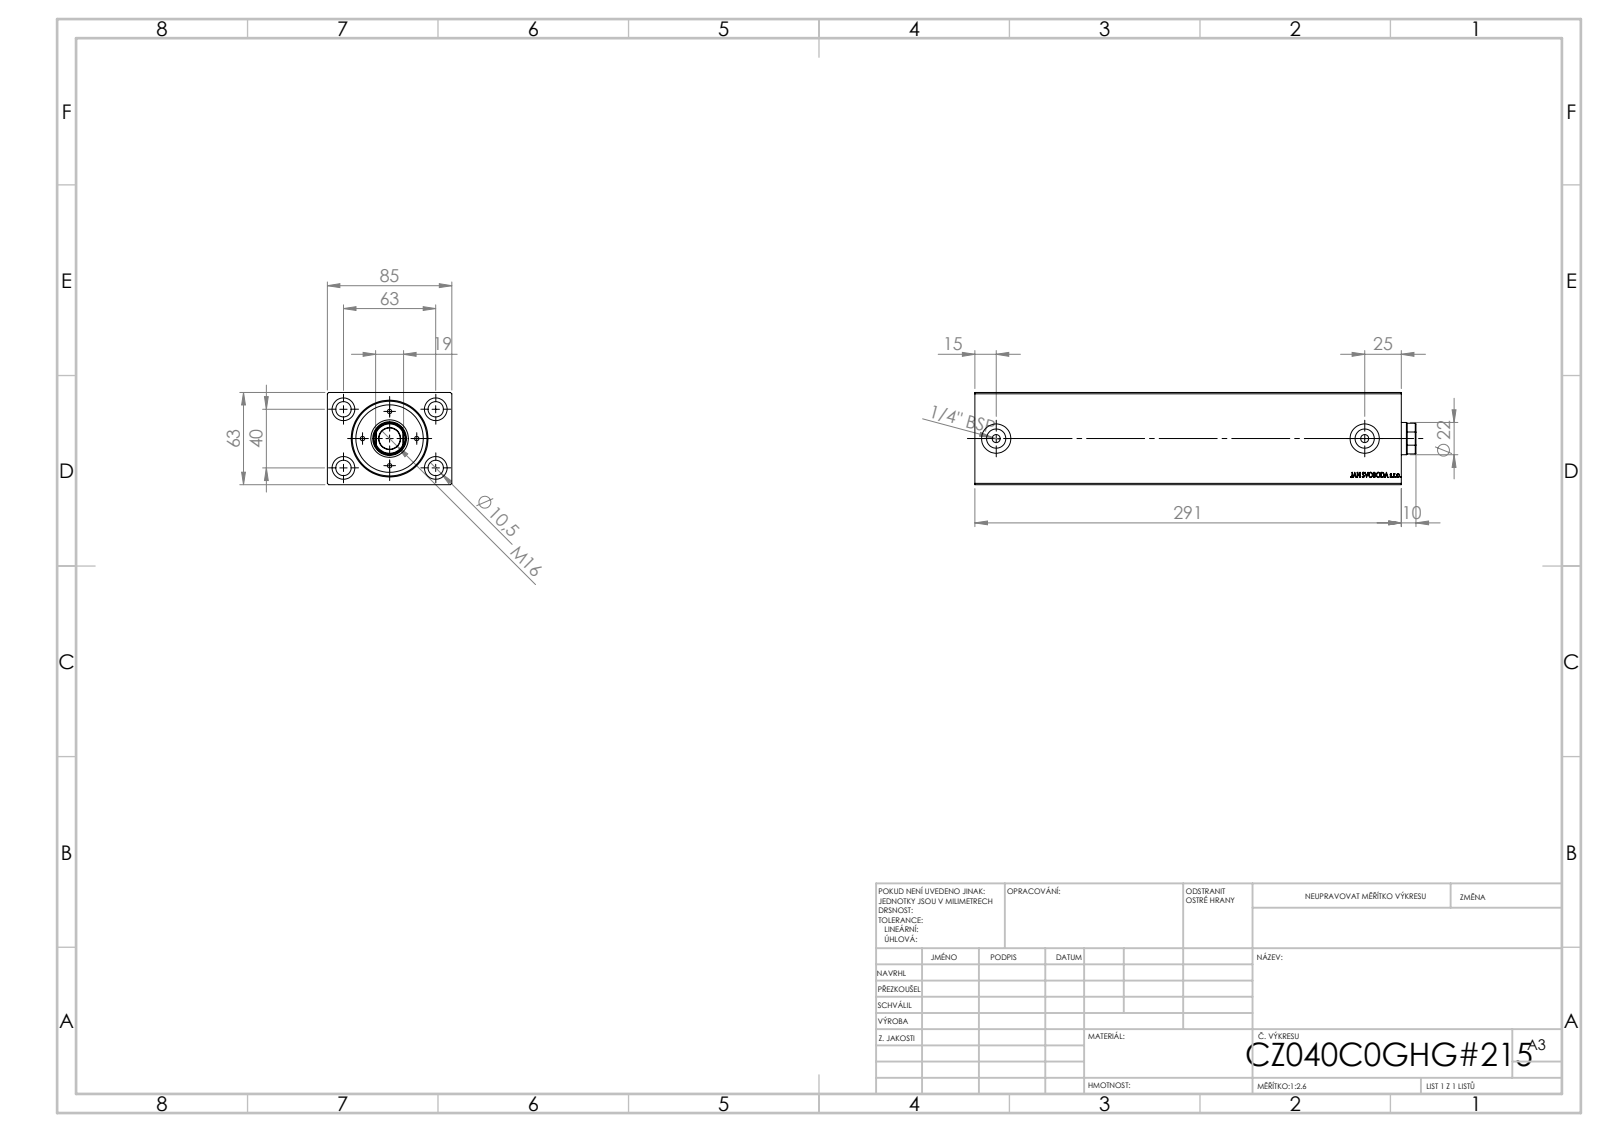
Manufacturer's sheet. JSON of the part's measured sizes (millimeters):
{"step_written_by": "SolidWorks 2019 (CONFIG_CONTROL_DESIGN)", "units": "millimeters", "bodies": {"solids": 1, "faces": 825, "planar": 397, "cylindrical": 46, "other": 382}, "overall_size": [291, 85, 63], "volume_mm3": 1090000, "surface_area_mm2": 171682, "round_holes": [[10.5, 4], [15.5, 4], [5.5, 2], [8, 2], [13.16, 2], [20, 2], [36, 1], [40, 1], [51, 1]], "face_to_face_distances": [63, 85, 291, 275.7, 15.3, 290.8, 15.1, 103.22, 10.33, 280.67], "hole_center_spacings": [37.31, 40, 63, 74.63, 231.5, 251.5]}
